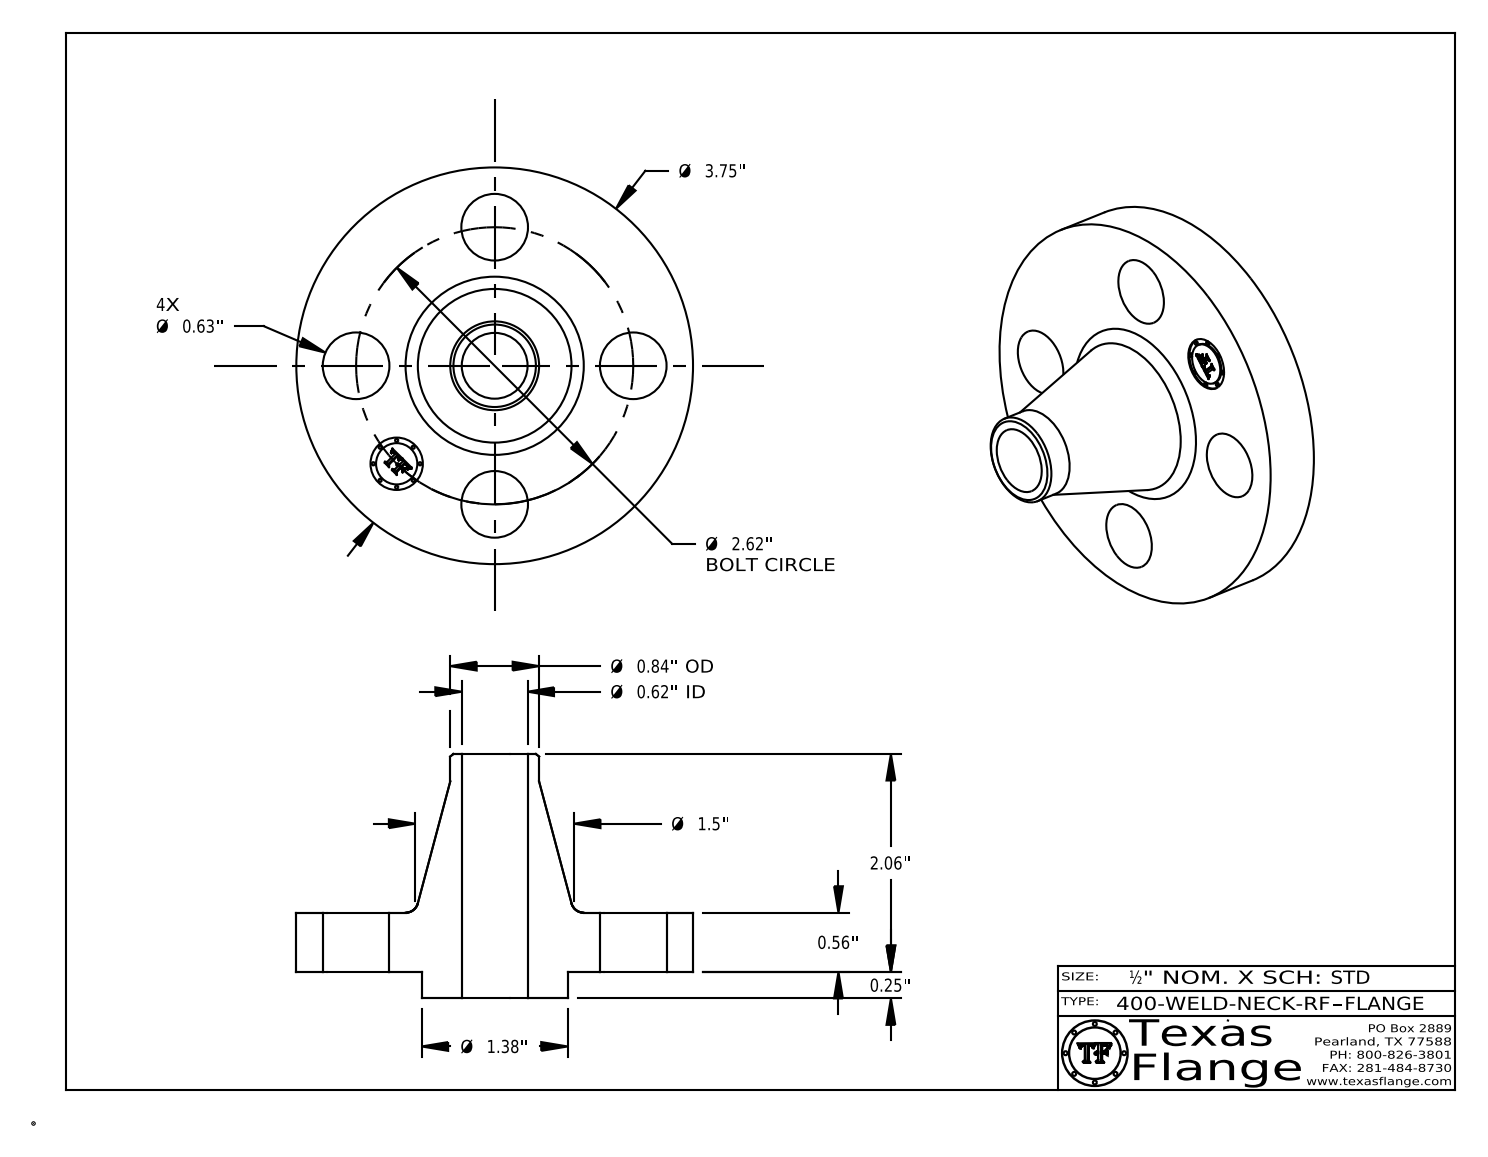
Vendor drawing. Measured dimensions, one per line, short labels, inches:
name: 400-WELD-NECK-RF
written by: CATIA V5 STEP AP214 (AUTOMOTIVE_DESIGN)
unit: in
bodies: 1 solid, 411 faces (369 planar, 36 cylindrical, 6 other)
size: 3.75 × 3.75 × 2.31
volume: 6.677 in³; area: 39.73 in²
holes: 4× ⌀0.63, 1× ⌀0.495, 1× ⌀0.622
bosses: 8× ⌀0.03, 1× ⌀3.75, 1× ⌀1.38, 1× ⌀0.84, 1× ⌀0.39
face distances: 0.56, 0.25, 0.81, 2.31, 2.06, 1.5, 0.795, 0.545, 0.015, 1.515
hole spacings: 1.31, 1.852, 1.003, 2.42, 2.62, 1.31
